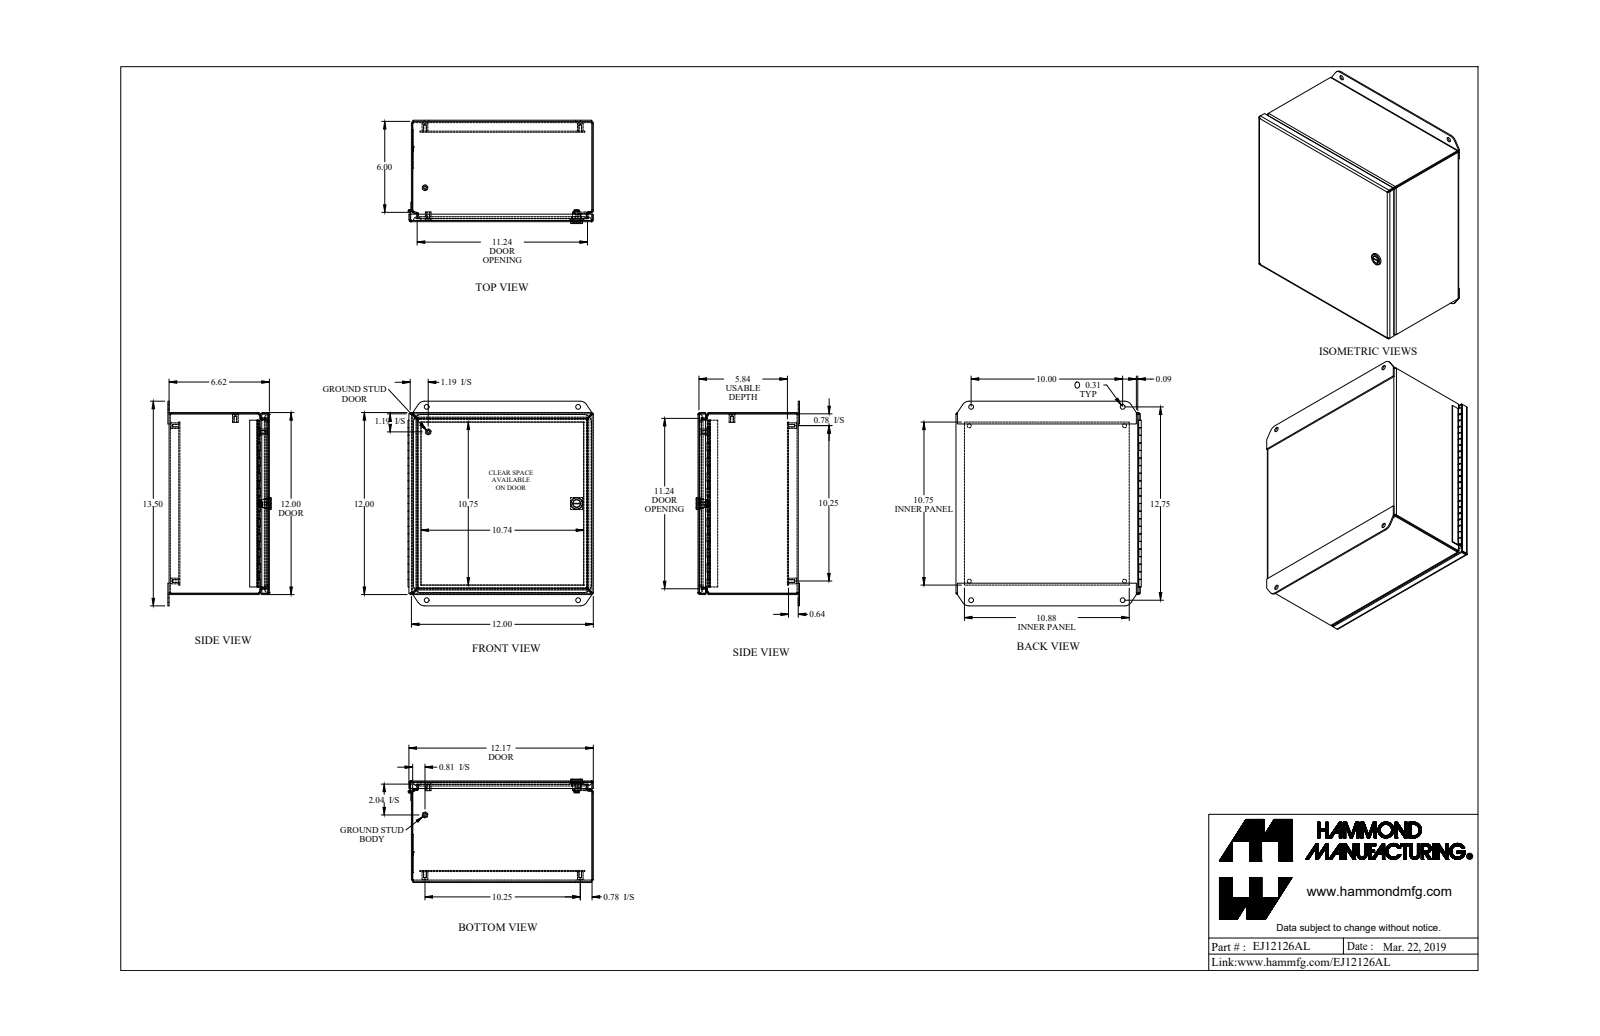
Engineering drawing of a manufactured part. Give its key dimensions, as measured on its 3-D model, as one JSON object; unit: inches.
{"part_name": "EJ12126AL_Default", "step_written_by": "SolidWorks 2019 (CONFIG_CONTROL_DESIGN)", "units": "inches", "bodies": {"solids": 14, "faces": 658, "planar": 432, "cylindrical": 158, "other": 68}, "overall_size": [13.5, 12.226, 6.82], "volume_in3": 66.75, "surface_area_in2": 1701, "round_holes": [[0.159, 6], [0.265, 4], [0.313, 4], [0.516, 1]], "round_bosses_or_shafts": [[0.375, 6], [0.33, 6], [0.788, 1], [0.535, 1], [0.496, 1], [0.435, 1], [0.18, 1], [0.1, 1]], "partial_cylinders_radius": [[0.041, 16], [0.121, 16], [0.281, 12], [0.25, 4], [0.499, 4], [0.5, 4], [0.06, 2], [0.03, 1]], "face_to_face_distances": [0.081, 6.536, 11.919, 6.617, 12, 11.838, 6.455, 0.643, 0.562, 5.974], "hole_center_spacings": [1.256, 10.202, 10.233, 10.25, 10.25, 10.267, 11.501, 14.496]}
